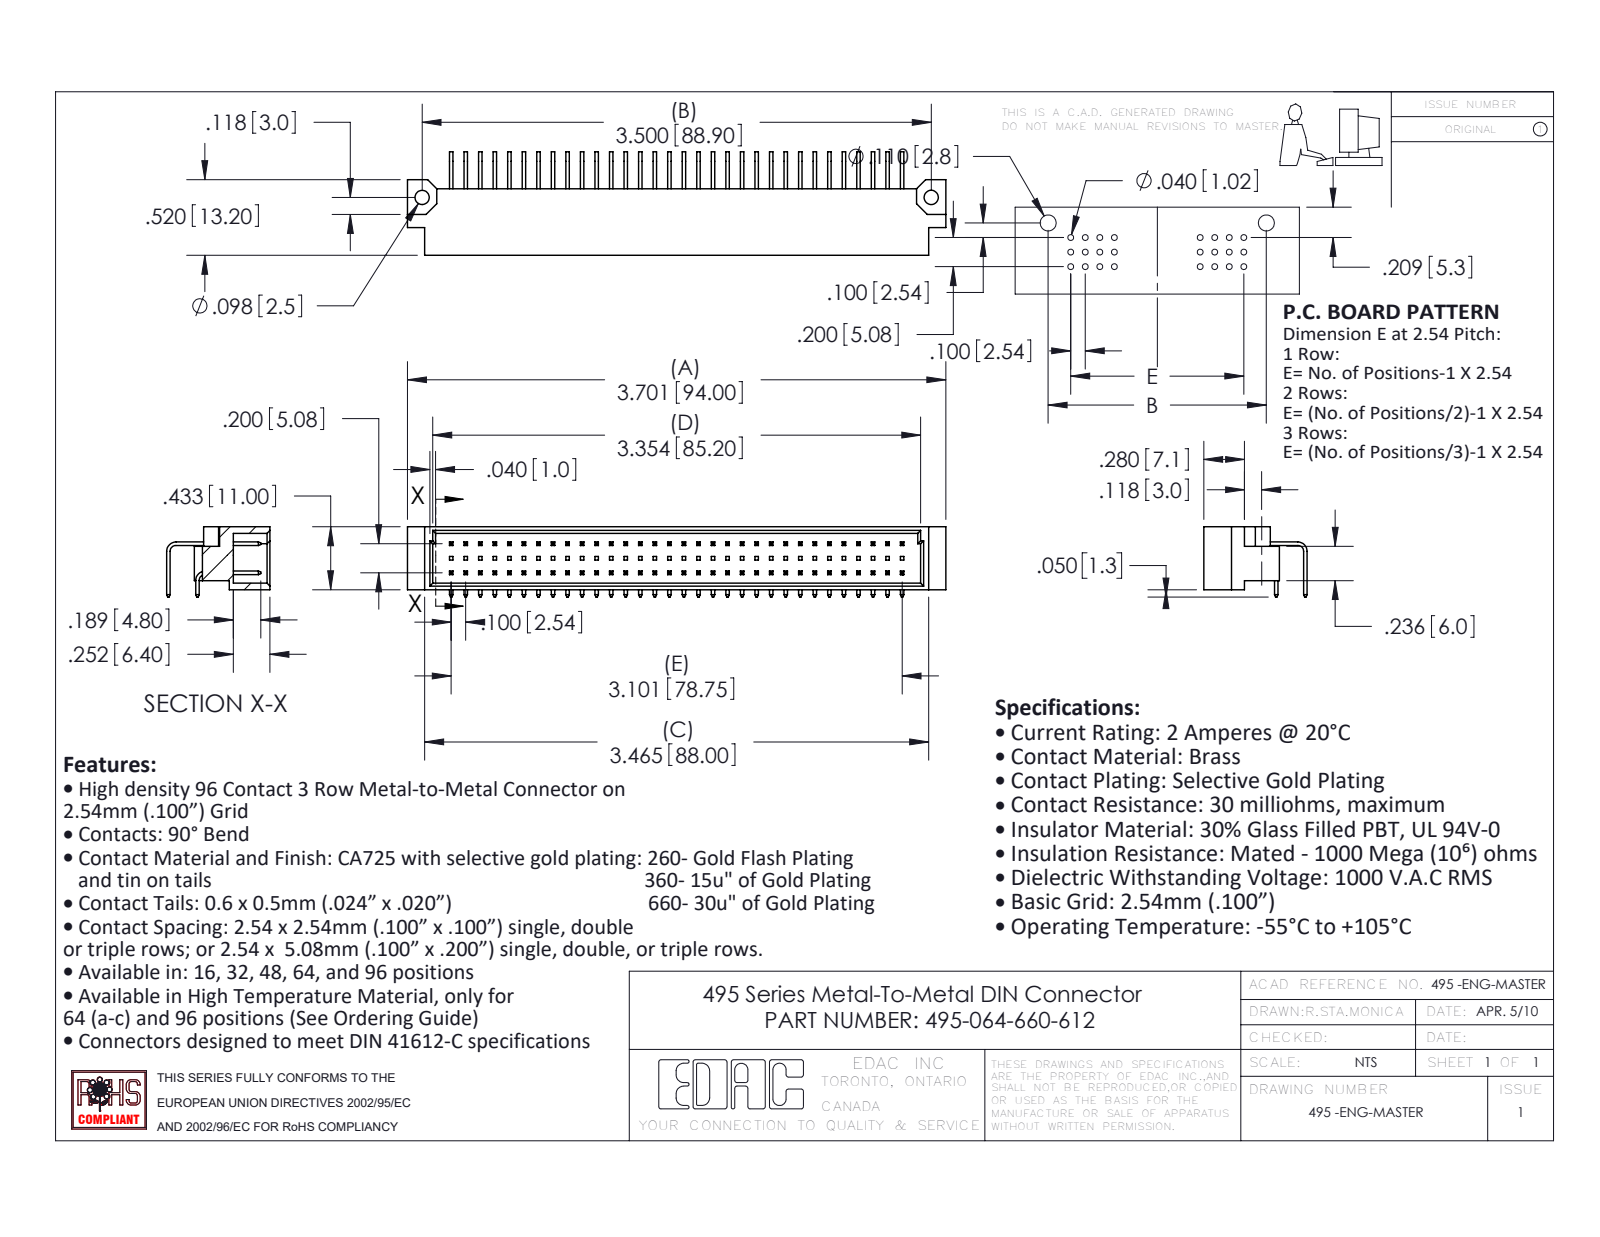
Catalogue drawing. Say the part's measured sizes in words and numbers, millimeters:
The part is named "495 Part_96; 495-290-1; 495-064-660-612; 495-290-3". Its 3-D file was written by "SolidWorks 2020 (AUTOMOTIVE_DESIGN)". It is 65 solids with 1585 faces: 1453 planar, 132 cylindrical and 0 other. Overall it measures 94 by 18.05 by 12.27 millimeters. Its volume is 6 391 cubic millimeters and its surface area 9 910 square millimeters. Round holes: 2 of diameter 2.49. Partial cylindrical surfaces (rounded edges, fillets, slot ends): 2 of radius 1.02, 2 of radius 1.65. The main face-to-face distances are 1.14, 9.86, 0.61, 5.08, 5.2, 11, 2.54, 8.72, 1.6, 9.4. The hole center spacings are 88.9.
